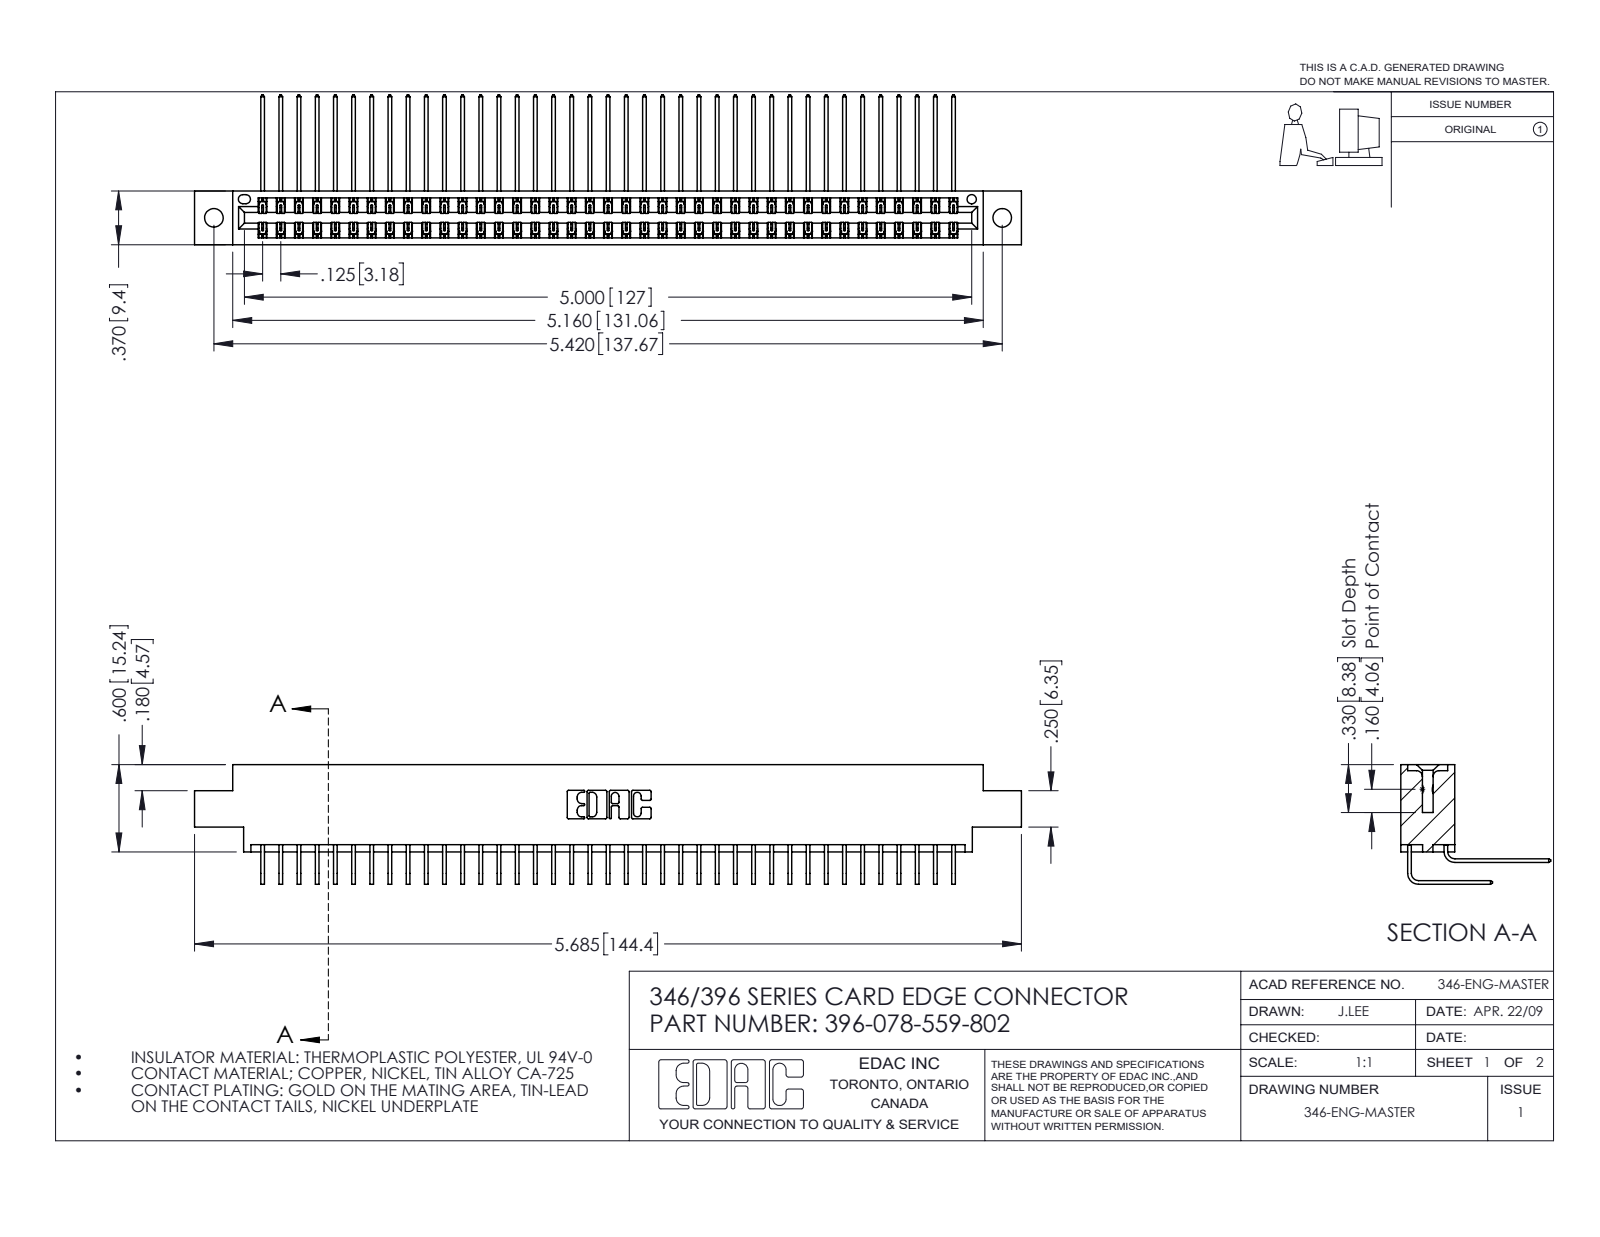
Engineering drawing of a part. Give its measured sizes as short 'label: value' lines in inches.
name: 396-078-559-802; 346 Part_0.170 Offset - 0.128 Dia; 345-292-001_559 Tail - 2; 345-292-001_558 559 Tail - 1
written by: SolidWorks 2016 (CONFIG_CONTROL_DESIGN)
unit: in
bodies: 79 solids, 4338 faces (2966 planar, 1372 cylindrical, 0 other)
size: 5.685 × 1.03 × 0.823
volume: 0.874 in³; area: 33.64 in²
holes: 2× ⌀0.128, 1× ⌀0.064
rounds: 117× R0.006, 22× R0.01, 6× R0.007, 6× R0.031, 3× R0.026, 2× R0.014, 2× R0.022, 2× R0.024
face distances: 0.048, 0.322, 0.025, 0.37, 0.25, 0.072, 0.298, 0.275, 0.148, 0.222
hole spacings: 0.246, 5.211, 5.42
